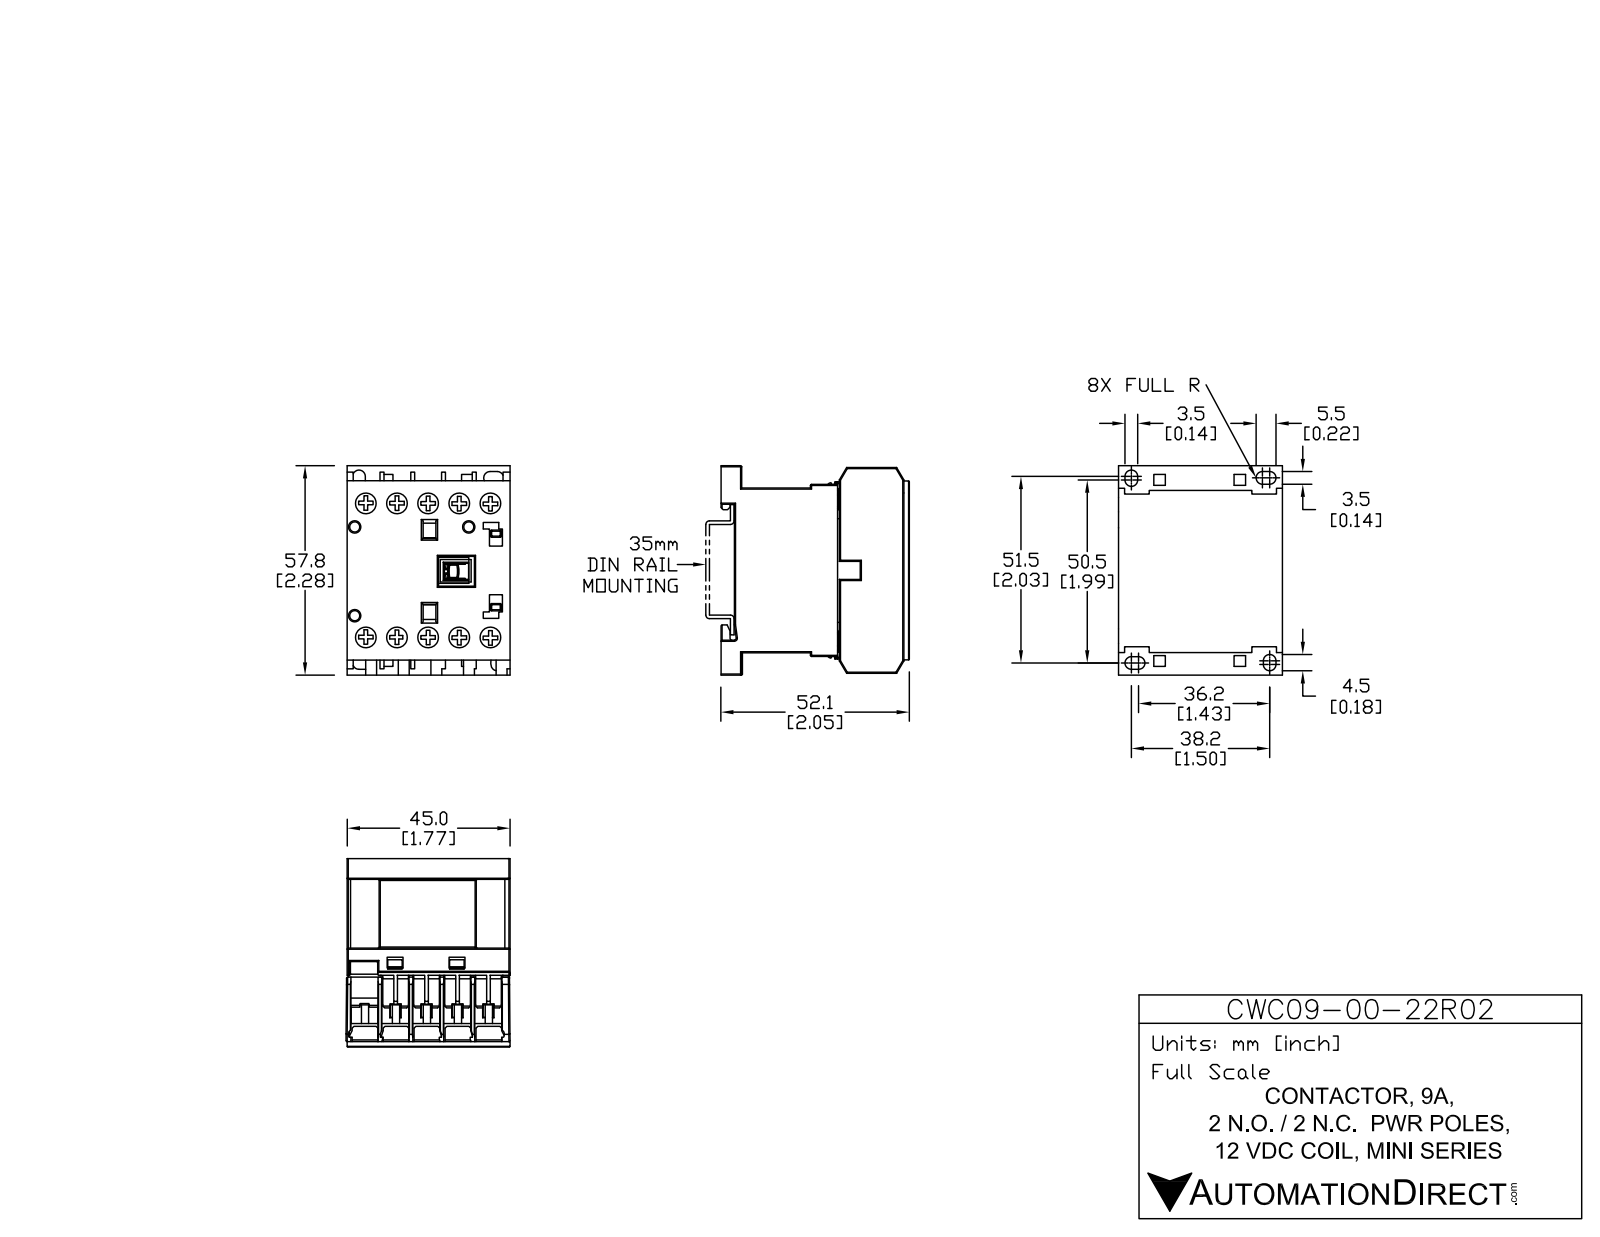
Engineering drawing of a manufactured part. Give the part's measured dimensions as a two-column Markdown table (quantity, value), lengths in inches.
| quantity | value |
| --- | --- |
| part name | CWC09-00-22R02 |
| STEP written by | SolidWorks 2013 (AUTOMOTIVE_DESIGN) |
| units | inches |
| bodies | 15 solids, 535 faces (445 planar, 90 cylindrical, 0 other) |
| overall size | 2.285 × 2.052 × 1.801 |
| volume | 5.927 in³ |
| surface area | 47.18 in² |
| round holes (diameter × count) | 0.244 × 10, 0.11 × 3 |
| round bosses / shafts (diameter × count) | 0.232 × 10 |
| partial cylindrical surfaces (radius × count) | 0.012 × 20, 0.068 × 6, 0.068 × 2, 0.013 × 1, 0.017 × 1, 0.022 × 1 |
| main face-to-face distances | 0.325, 1.791, 0.049, 0.65, 0.374, 0.217, 0.699, 0.202, 0.419, 0.276 |
| hole center spacings | 0.337, 1.494, 0.673, 1.603, 1.455, 1.01, 1.771, 0.272 |
